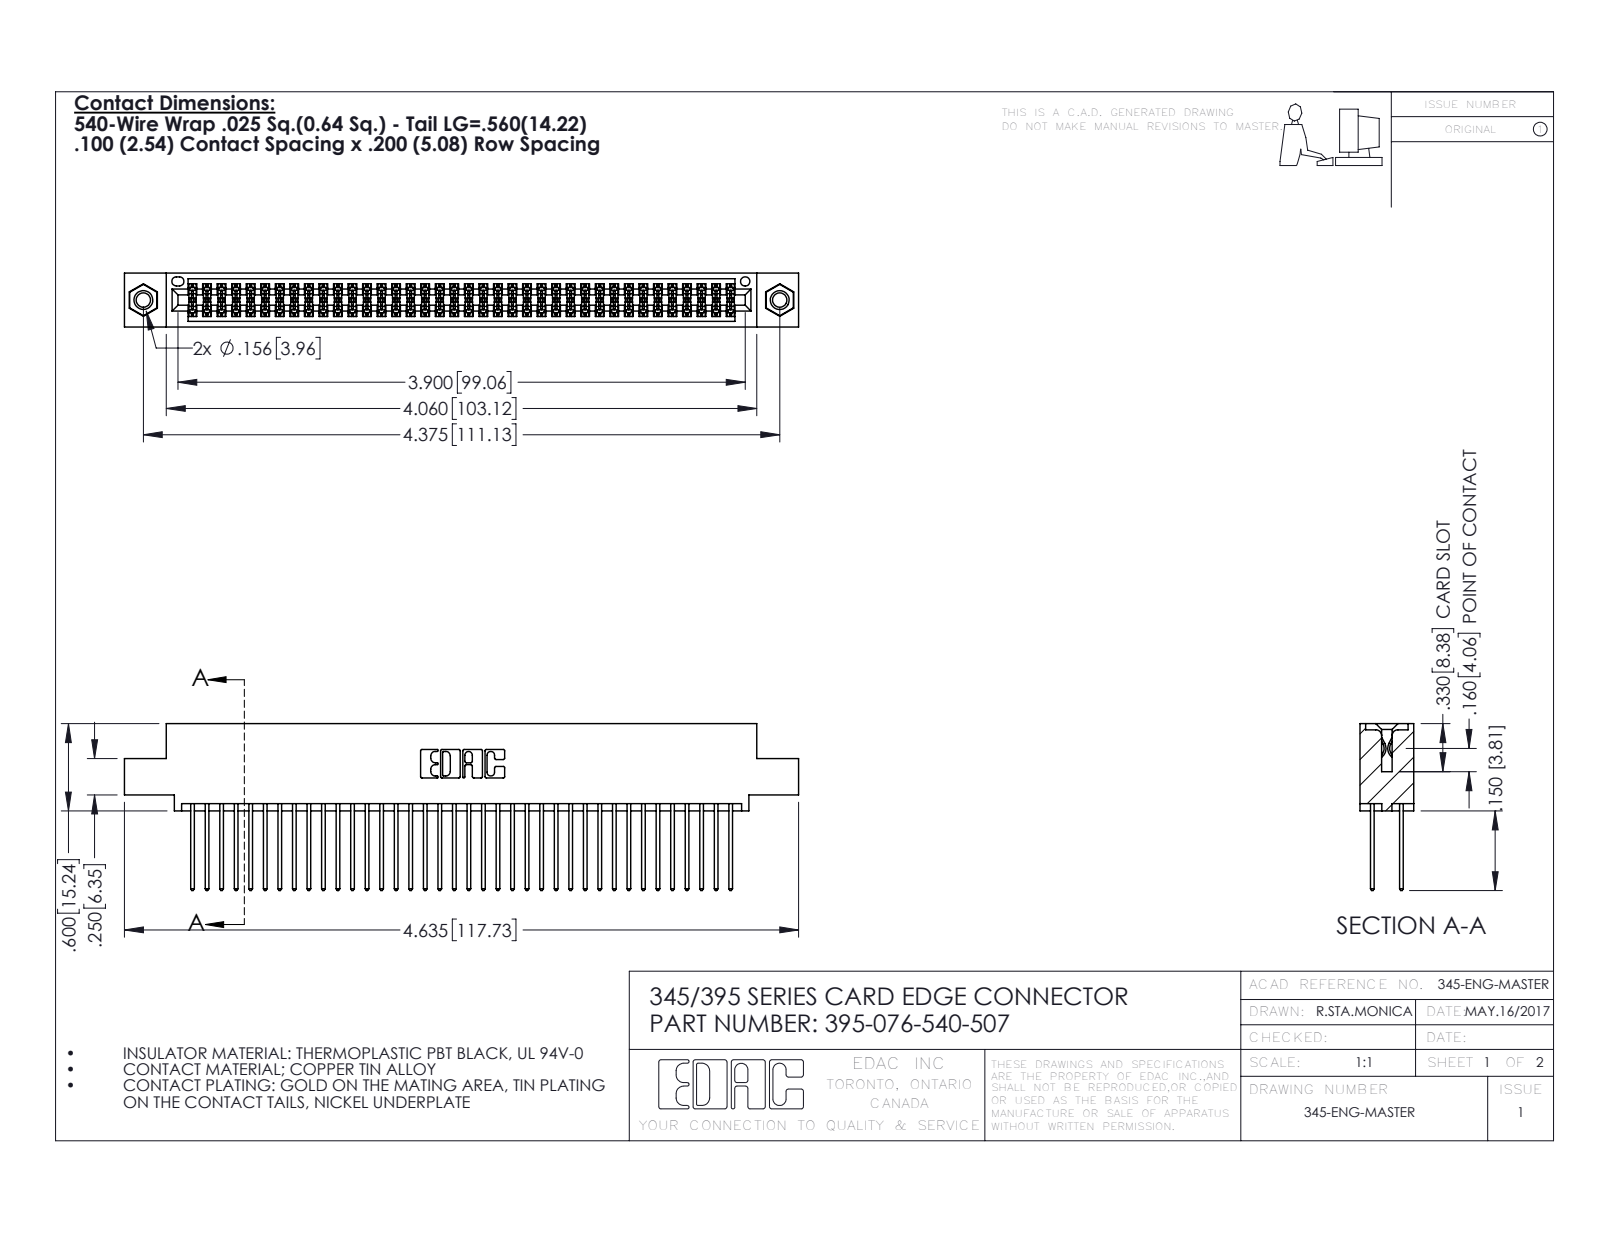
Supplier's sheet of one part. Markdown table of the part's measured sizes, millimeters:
| quantity | value |
| --- | --- |
| part name | 395-076-540-507; 345 Part_0.110 Offset - 0.156 Dia-TI; 345-250-001_345-250-005-103; 345-292-001_345-293-140 |
| STEP written by | SolidWorks 2016 (CONFIG_CONTROL_DESIGN) |
| units | millimeters |
| bodies | 79 solids, 3990 faces (2624 planar, 1350 cylindrical, 16 other) |
| overall size | 117.7 × 29.1 × 9.4 |
| volume | 11 600 mm³ |
| surface area | 18 530 mm² |
| round holes (diameter × count) | 2.5 × 2, 3.2 × 2, 4 × 2, 1.6 × 1 |
| round bosses / shafts (diameter × count) | 3.9 × 2 |
| partial cylindrical surfaces (radius × count) | 0.2 × 114, 0.3 × 76, 0.3 × 22, 0.2 × 6, 0.8 × 6, 0.7 × 3, 0.4 × 2, 0.5 × 2 |
| main face-to-face distances | 1.8, 7.6, 5.1, 2.5, 6.9, 0.6, 9.4, 5.7, 4.4, 3.8 |
| hole center spacings | 6.9, 105.1, 111.1 |
